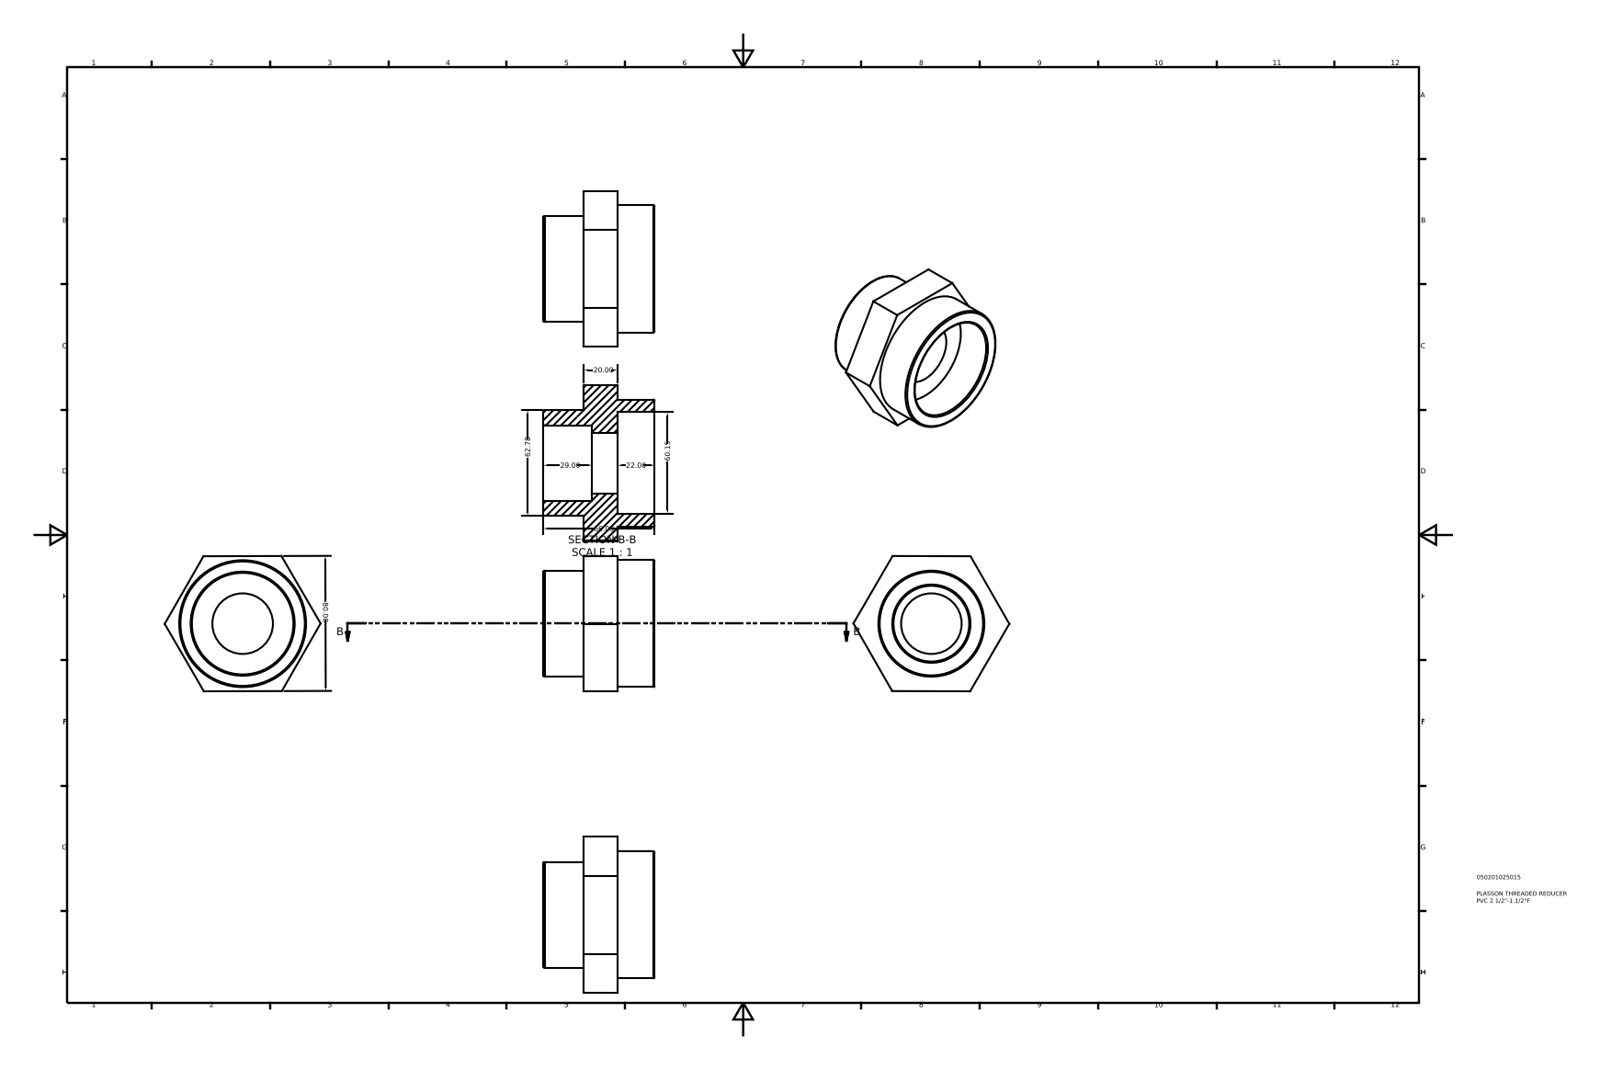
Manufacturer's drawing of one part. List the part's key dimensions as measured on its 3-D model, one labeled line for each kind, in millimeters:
Part name (STEP PRODUCT): 050201025015
STEP written by: Autodesk Inventor 2015 (AUTOMOTIVE_DESIGN)
Units: millimetres
Bodies: 1 solid, 21 faces (12 planar, 5 cylindrical, 4 other)
Overall size (bounding box): 92.38 × 80.14 × 66
Volume: 159 251 mm³ · Surface area: 34 223 mm²
Round holes (diameter × count): ⌀35.88 ×1, ⌀44.84 ×1, ⌀60.15 ×1
Round bosses / shafts (diameter × count): ⌀75.18 ×1, ⌀62.78 ×1
Main face-to-face distances: 20, 42, 22, 24, 44, 66, 80, 80.06, 80.04, 29
